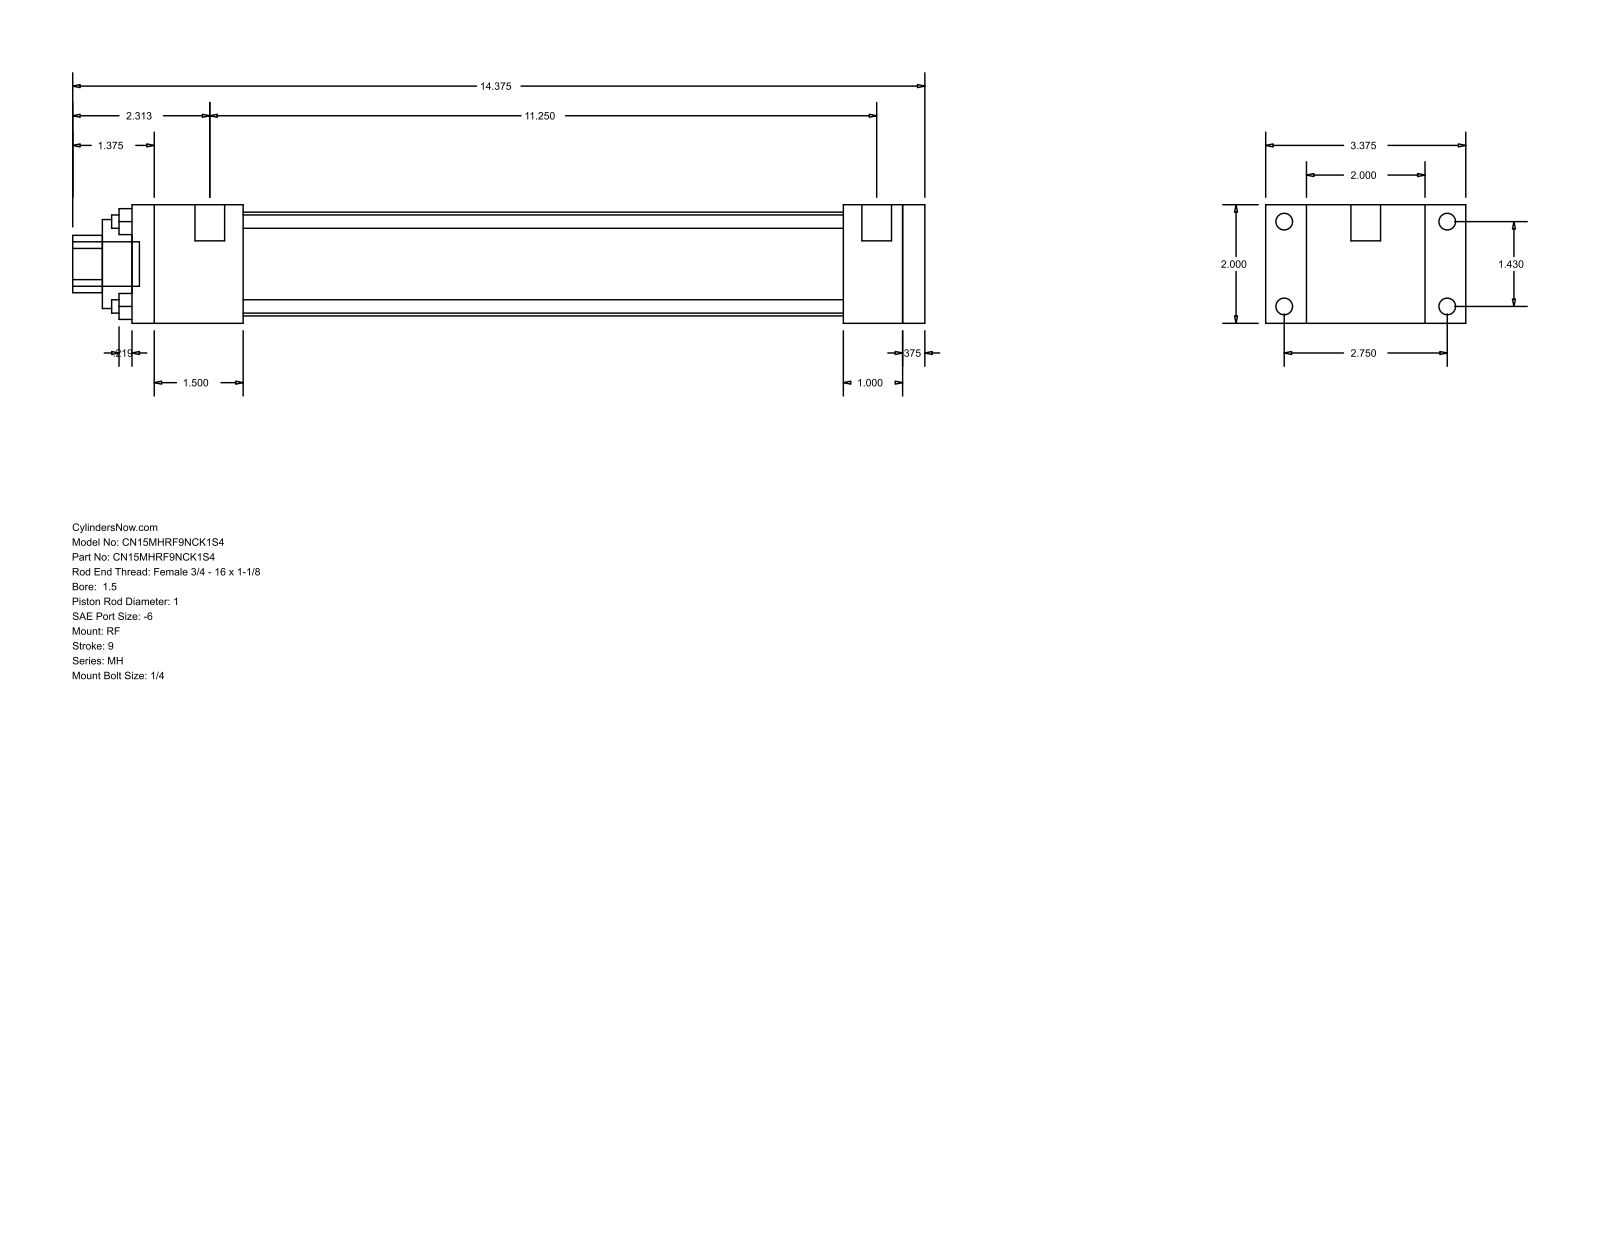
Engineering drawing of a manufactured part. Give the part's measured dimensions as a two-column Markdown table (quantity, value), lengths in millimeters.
| quantity | value |
| --- | --- |
| part name | MH_RF__0150_1 |
| STEP written by | GSSL Pune (CONFIG_CONTROL_DESIGN) |
| units | millimeters |
| bodies | 0 solids, 92 faces (64 planar, 28 cylindrical, 0 other) |
| overall size | 365.12 × 85.72 × 50.8 |
| round holes (diameter × count) | 5.71 × 4, 25.4 × 1, 38.1 × 1, 44.45 × 1 |
| round bosses / shafts (diameter × count) | 7.14 × 4, 5.56 × 4, 12.7 × 2, 19.05 × 1 |
| partial cylindrical surfaces (radius × count) | 12.29 × 1 |
| main face-to-face distances | 50.8, 9.52, 330.2, 25.4, 339.72, 17.46, 68.26, 304.8, 34.92, 47.63 |
| hole center spacings | 25.68, 36.32, 51.36 |
